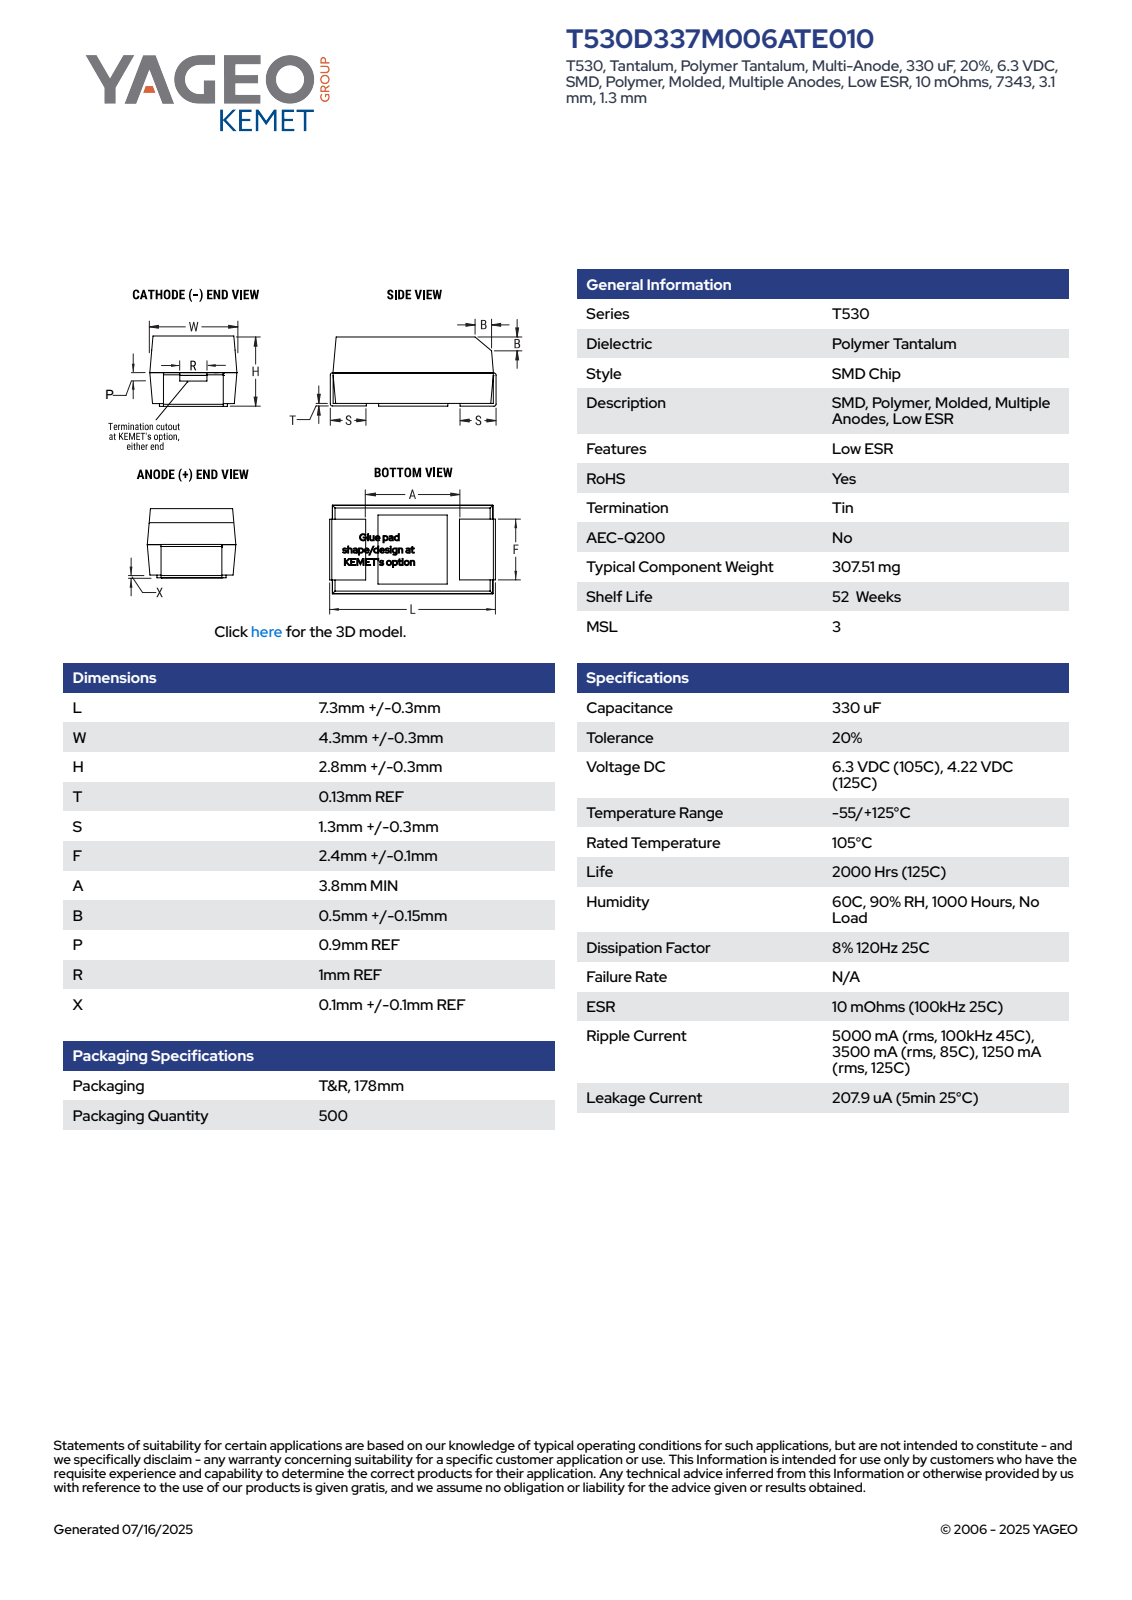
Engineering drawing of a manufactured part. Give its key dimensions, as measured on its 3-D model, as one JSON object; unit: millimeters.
{"part_name": "CTSM_TCM2NKKO_7343_L7.6W4.6H3.1T0.13S1.3F2.5A3.6B0.65P0.9R1X0.1", "step_written_by": "SolidWorks 2021 (AUTOMOTIVE_DESIGN)", "units": "millimeters", "bodies": {"solids": 4, "faces": 100, "planar": 95, "cylindrical": 5, "other": 0}, "overall_size": [7.6, 4.6, 3.13], "volume_mm3": 94, "surface_area_mm2": 144, "partial_cylinders_radius": [[0.1, 4]], "face_to_face_distances": [3, 3.1, 4.54, 4.53, 3.13, 7.47, 7.6, 7.34, 2.4, 5.2]}
